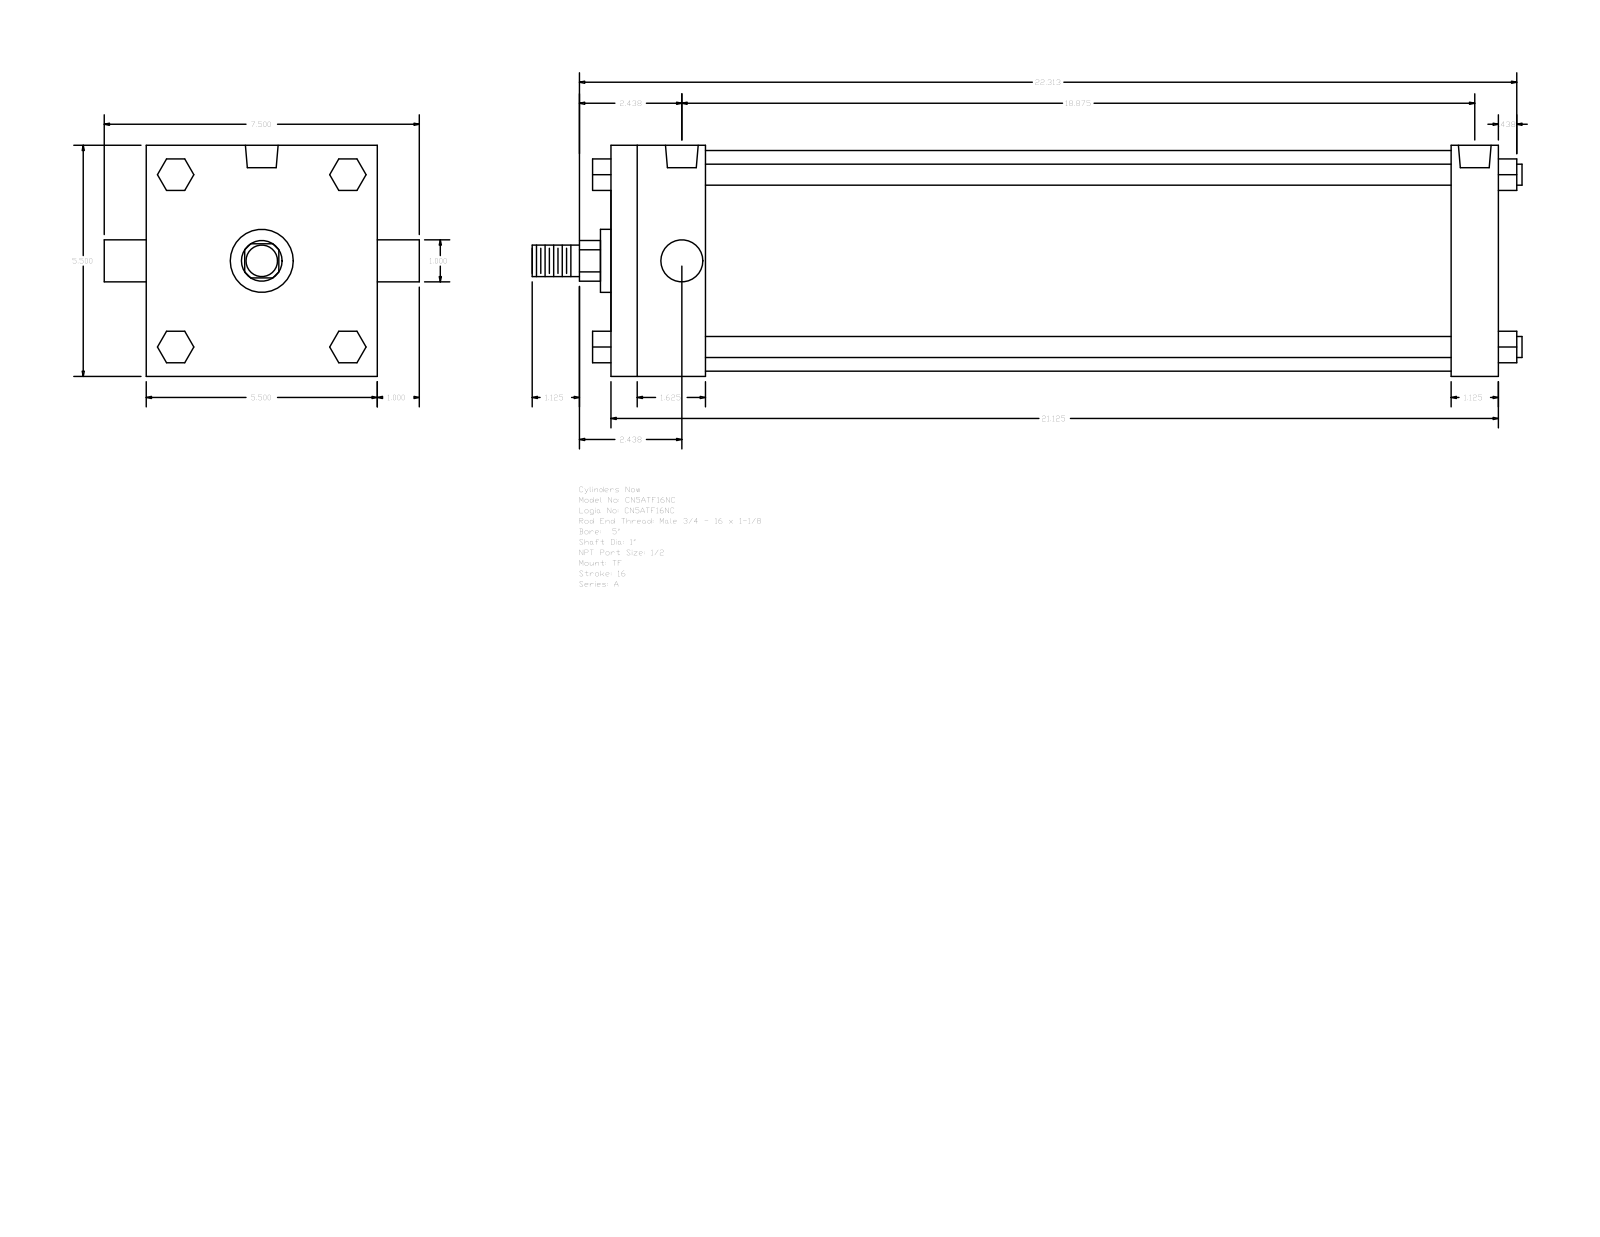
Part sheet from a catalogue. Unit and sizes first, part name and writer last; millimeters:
Units: millimetres
Overall size (bounding box): 598.49 × 190.5 × 139.7
Round holes (diameter × count): ⌀8.73 ×3, ⌀19.77 ×2
Round bosses / shafts (diameter × count): ⌀12.7 ×4, ⌀25.4 ×2, ⌀133.35 ×1, ⌀38.1 ×1, ⌀19.05 ×1
Partial cylindrical surfaces — rounded edges, fillets, slot ends (radius × count): R12.29 ×1
Main face-to-face distances: 139.7, 536.57, 28.57, 508, 57.15, 450.85, 479.42, 19.05, 52.07, 90.18
Hole centre spacings: 2.39, 477.04, 474.65, 479.43
Bodies: 0 solids, 120 faces (92 planar, 28 cylindrical, 0 other)
Part name (STEP PRODUCT): A_TF__0500_1
STEP written by: GSSL Pune (CONFIG_CONTROL_DESIGN)
